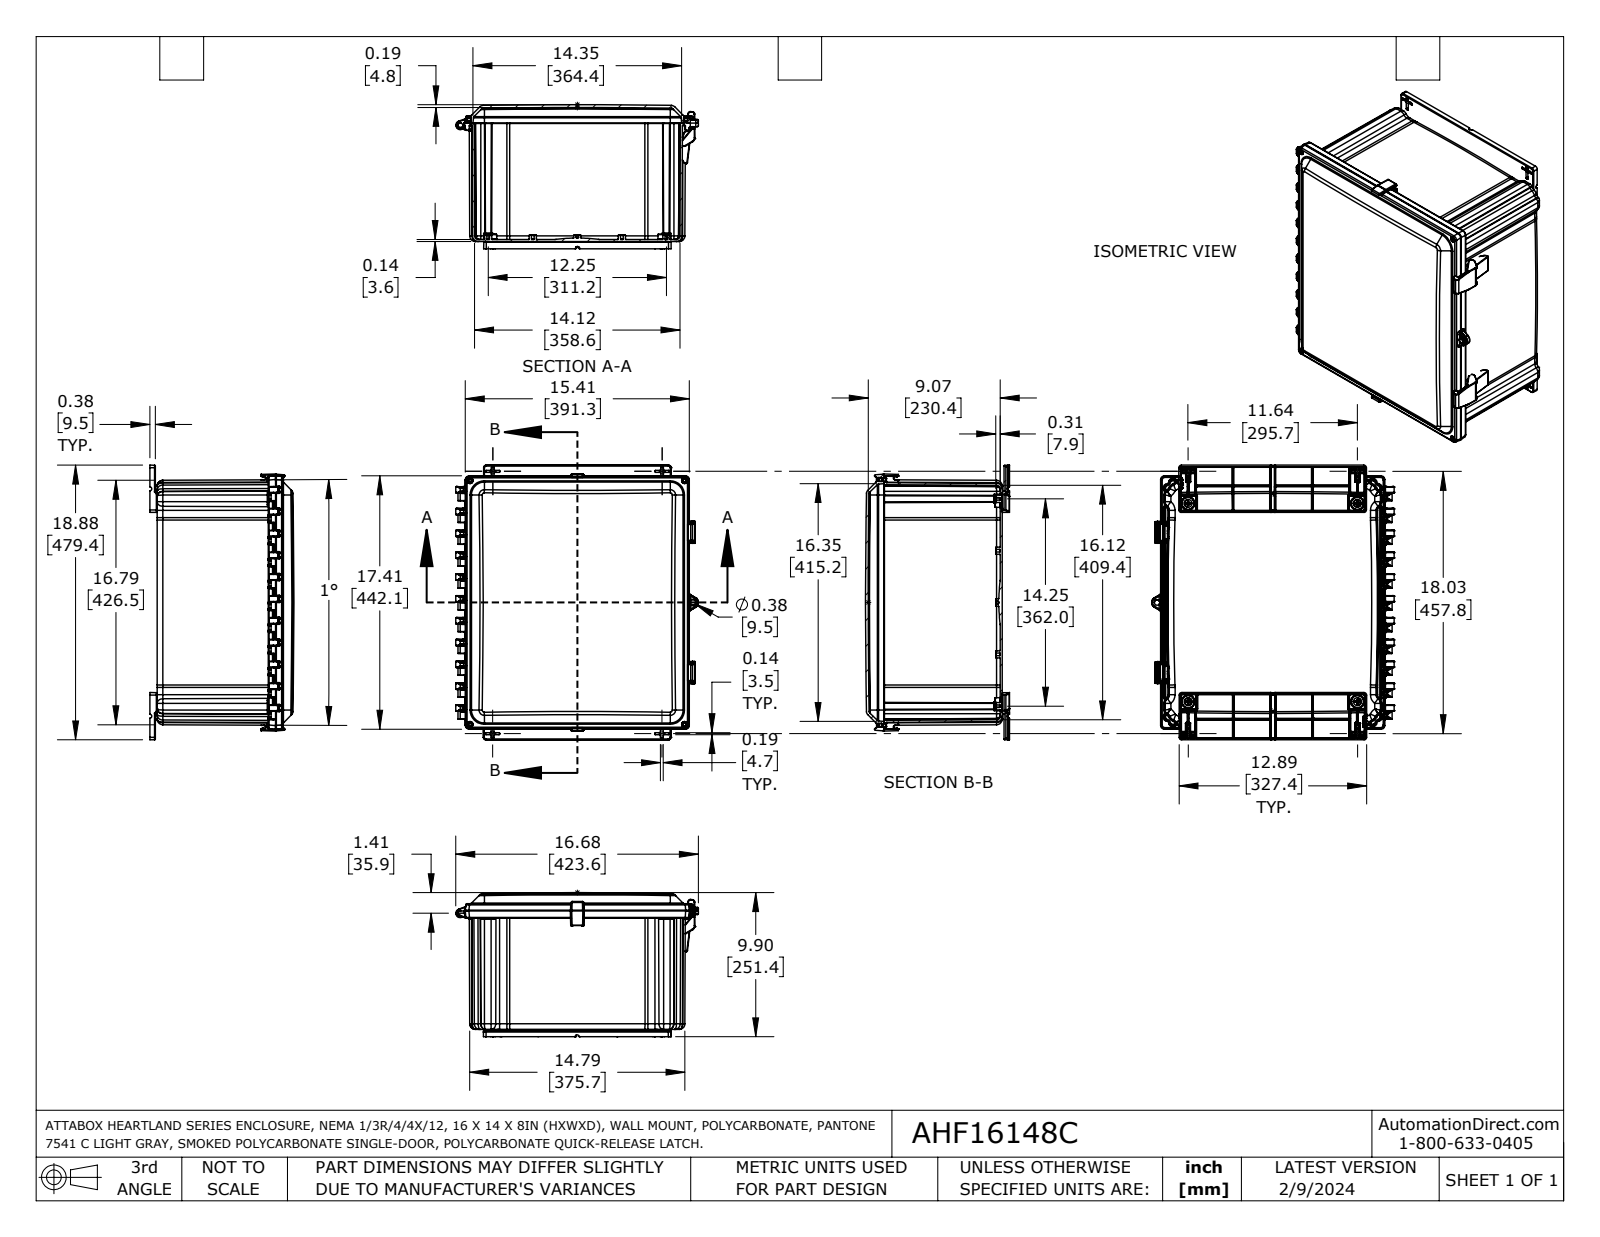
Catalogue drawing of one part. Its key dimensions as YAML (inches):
part_name: "AHF16148C"
step_written_by: "SolidWorks 2023 (AUTOMOTIVE_DESIGN)"
units: inches
bodies: {solids: 6, faces: 1858, planar: 657, cylindrical: 572, other: 629}
overall_size: [18.875, 16.676, 9.898]
volume: 213.8
surface_area: 2450
round_holes:
  - {diameter: 0.187, count: 21}
  - {diameter: 0.195, count: 4}
  - {diameter: 0.249, count: 4}
  - {diameter: 0.25, count: 4}
  - {diameter: 0.27, count: 4}
  - {diameter: 0.39, count: 4}
  - {diameter: 0.375, count: 2}
  - {diameter: 0.327, count: 1}
  - {diameter: 0.45, count: 1}
round_bosses_or_shafts:
  - {diameter: 0.487, count: 21}
  - {diameter: 0.625, count: 4}
  - {diameter: 0.25, count: 4}
  - {diameter: 0.2, count: 2}
  - {diameter: 0.313, count: 1}
partial_cylinders:
  - {radius: 0.035, count: 206}
  - {radius: 0.065, count: 31}
  - {radius: 0.01, count: 22}
  - {radius: 0.02, count: 21}
  - {radius: 0.346, count: 16}
  - {radius: 0.05, count: 8}
  - {radius: 0.404, count: 8}
  - {radius: 0.09, count: 4}
face_to_face_distances: [0.106, 0.14, 14.106, 16.106, 0.5, 14, 8.14, 16, 14.213, 8.64]
hole_center_spacings: [4.698, 7.755, 7.085, 9.396, 9.854, 12.318, 3.063, 3.562]
